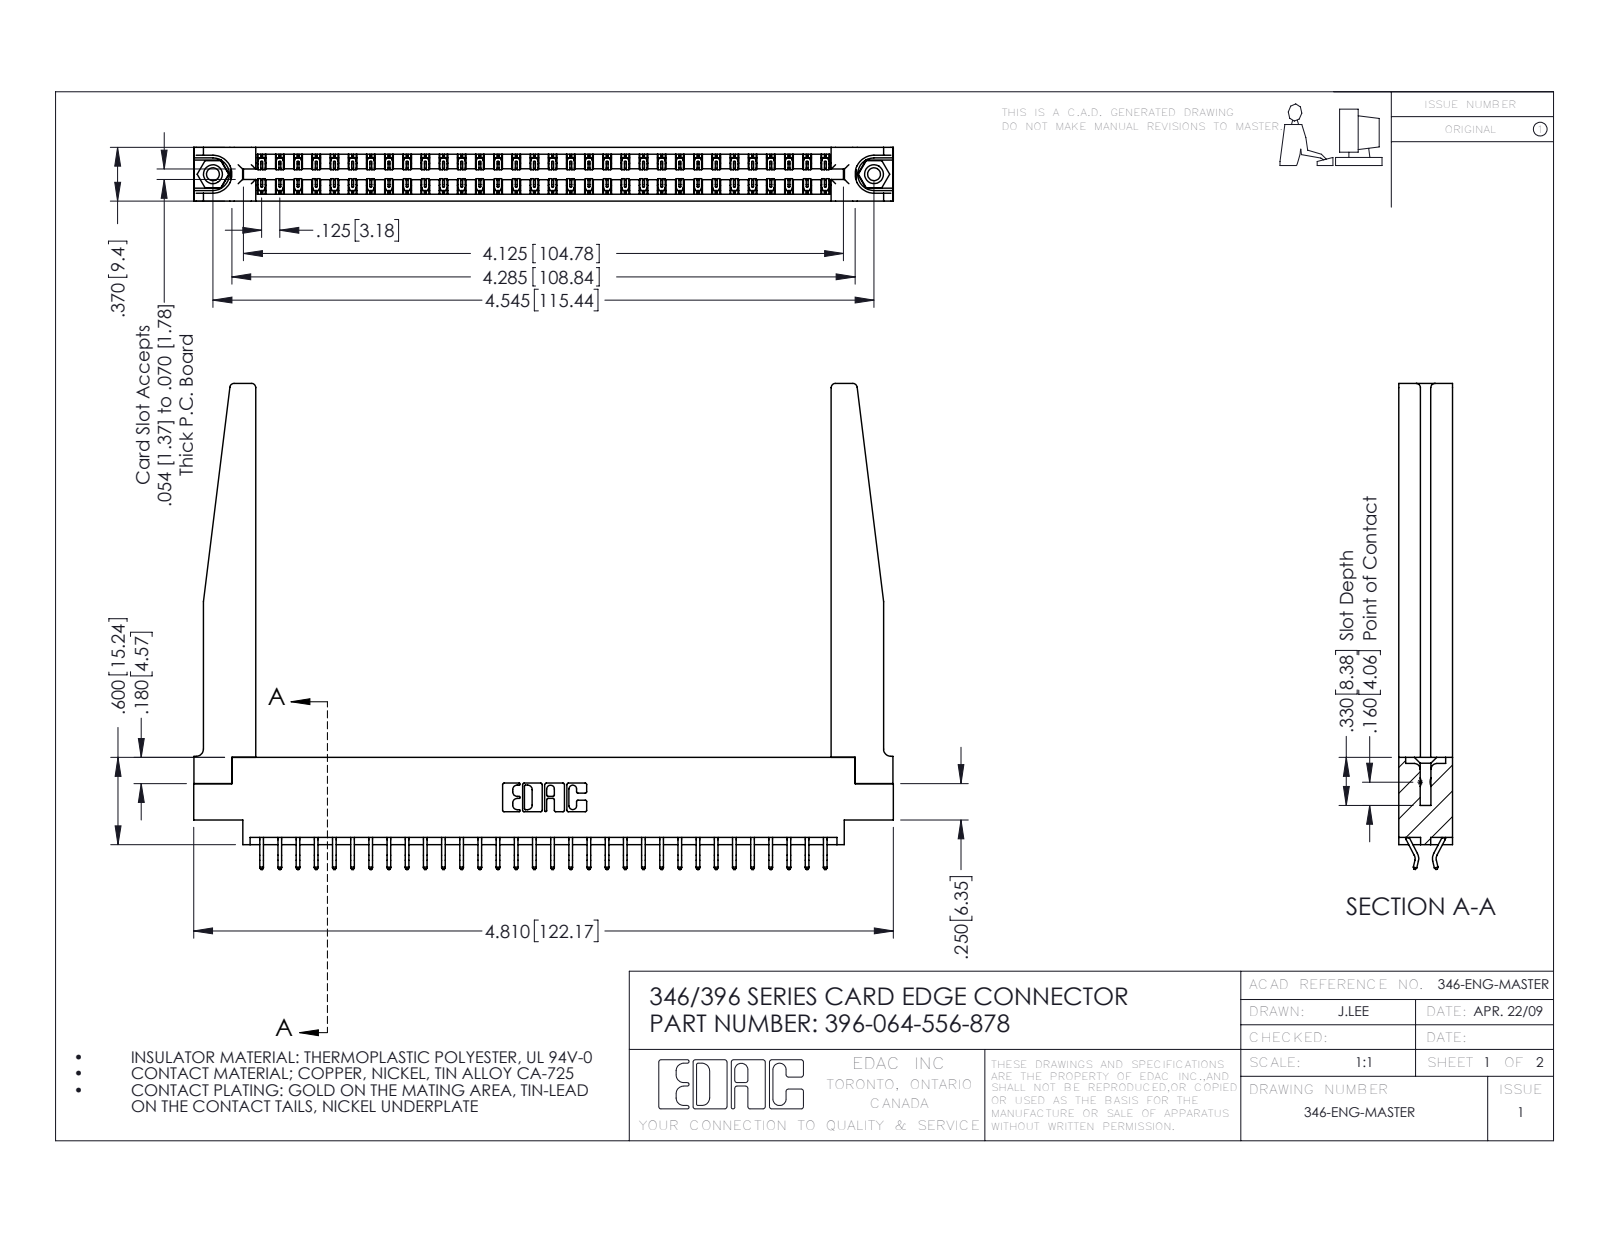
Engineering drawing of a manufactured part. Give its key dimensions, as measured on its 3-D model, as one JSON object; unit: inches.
{"part_name": "346 Part_0.170 Offset - 0.156 Dia-TH; 396-064-556-878; 346-220-078_345-220-078; 345-250-001_345-250-001-102 (+1 more)", "step_written_by": "SolidWorks 2016 (CONFIG_CONTROL_DESIGN)", "units": "inches", "bodies": {"solids": 69, "faces": 4072, "planar": 2718, "cylindrical": 1302, "other": 52}, "overall_size": [4.81, 3.34, 0.37], "volume_in3": 1.134, "surface_area_in2": 34.96, "round_holes": [[0.089, 2], [0.125, 2], [0.156, 2], [0.064, 1]], "round_bosses_or_shafts": [[0.155, 2]], "partial_cylinders_radius": [[0.006, 96], [0.01, 22], [0.03, 8], [0.007, 6], [0.031, 6], [0.05, 4], [0.026, 3], [0.01, 2]], "face_to_face_distances": [0.37, 0.048, 0.322, 0.072, 0.148, 0.15, 0.25, 0.025, 0.298, 0.275], "hole_center_spacings": [0.246, 4.337, 4.545]}
